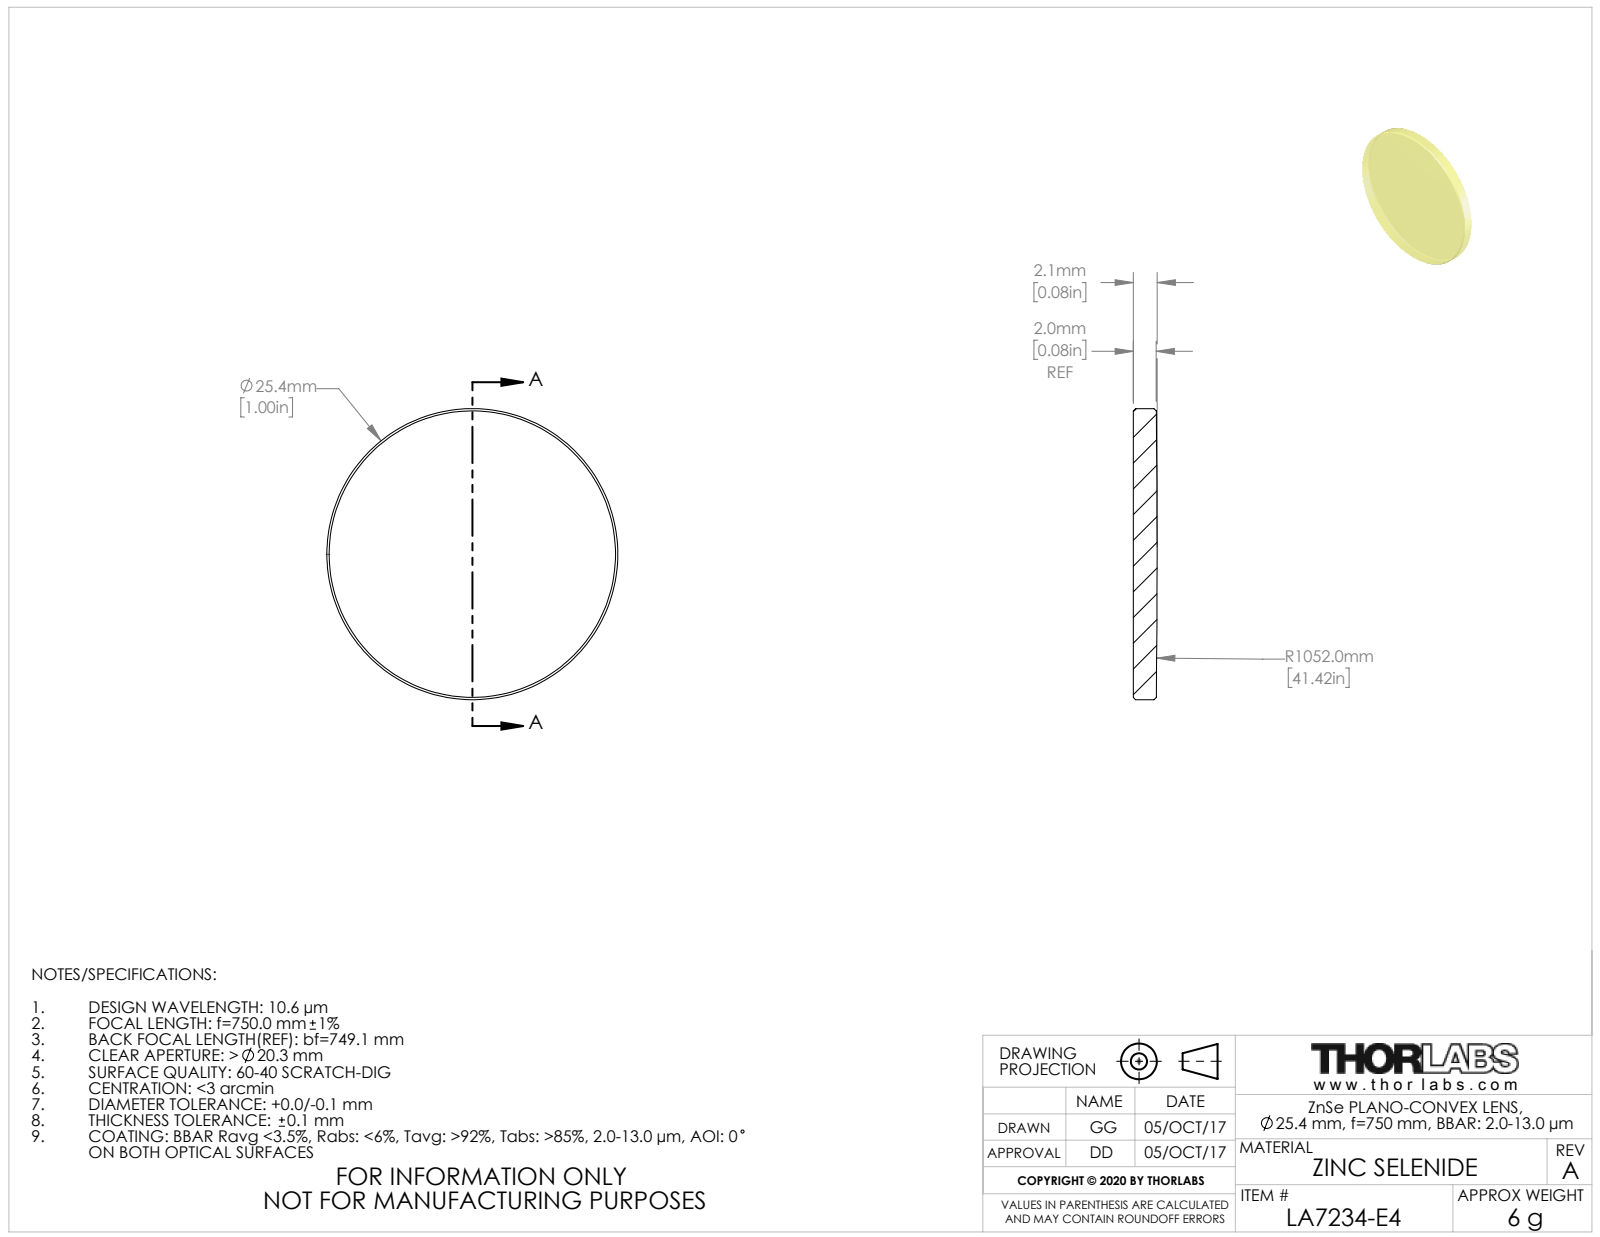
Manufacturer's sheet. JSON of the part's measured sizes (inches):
{"part_name": "TTN099113-E0W", "step_written_by": "SolidWorks 2018 (CONFIG_CONTROL_DESIGN)", "units": "inches", "bodies": {"solids": 1, "faces": 9, "planar": 1, "cylindrical": 2, "other": 6}, "overall_size": [1, 1, 0.082], "volume_in3": 0.063, "surface_area_in2": 1.79, "round_bosses_or_shafts": [[1, 1]]}
